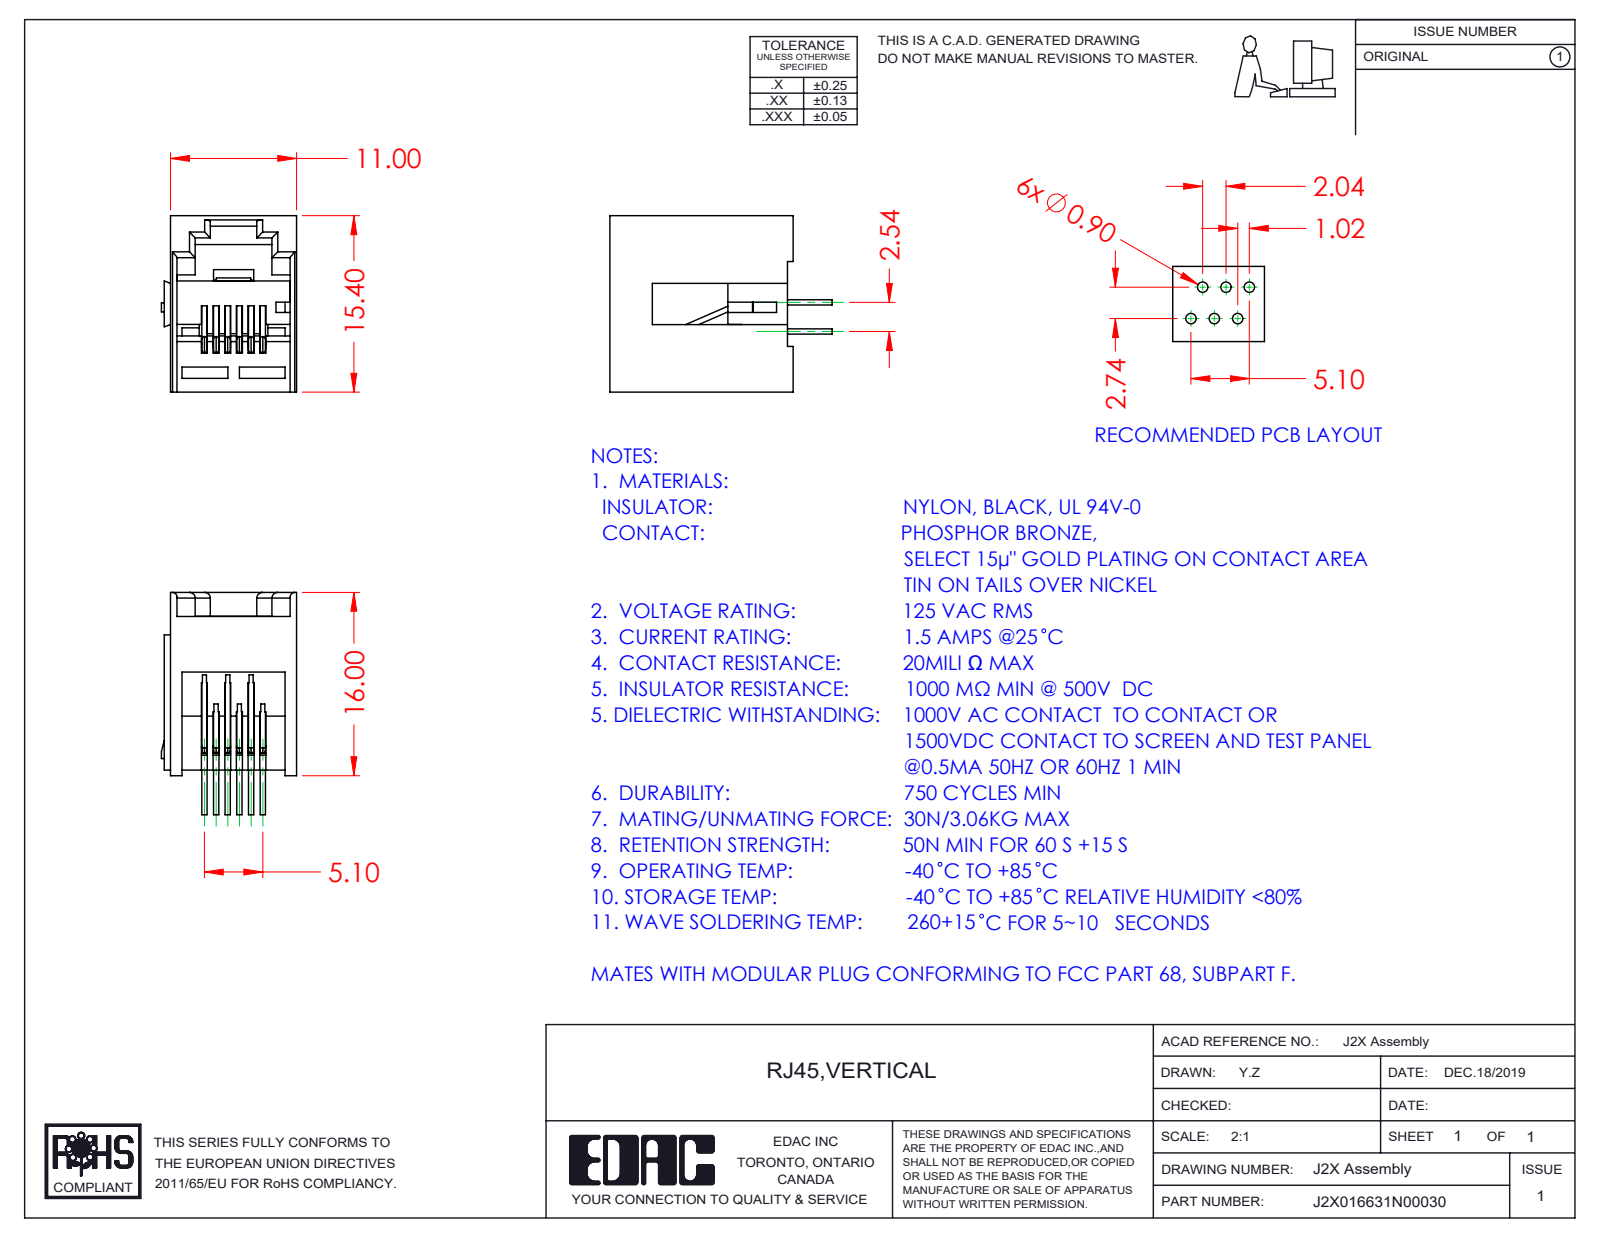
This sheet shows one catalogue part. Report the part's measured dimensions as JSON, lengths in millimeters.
{"part_name": "2X Contact Lock; 2X Insulator; J2X016631N00030; 2X Contacts", "step_written_by": "SolidWorks 2016 (CONFIG_CONTROL_DESIGN)", "units": "millimeters", "bodies": {"solids": 8, "faces": 466, "planar": 333, "cylindrical": 97, "other": 36}, "overall_size": [19.4, 15.4, 11.81], "volume_mm3": 1219, "surface_area_mm2": 2844, "round_bosses_or_shafts": [[0.46, 24]], "partial_cylinders_radius": [[0.5, 7], [0.15, 2], [0.3, 2], [0.4, 2], [0.2, 1]], "face_to_face_distances": [1, 11, 2.04, 1.02, 0.5, 0.56, 0.52, 10, 11.99, 10.44]}
